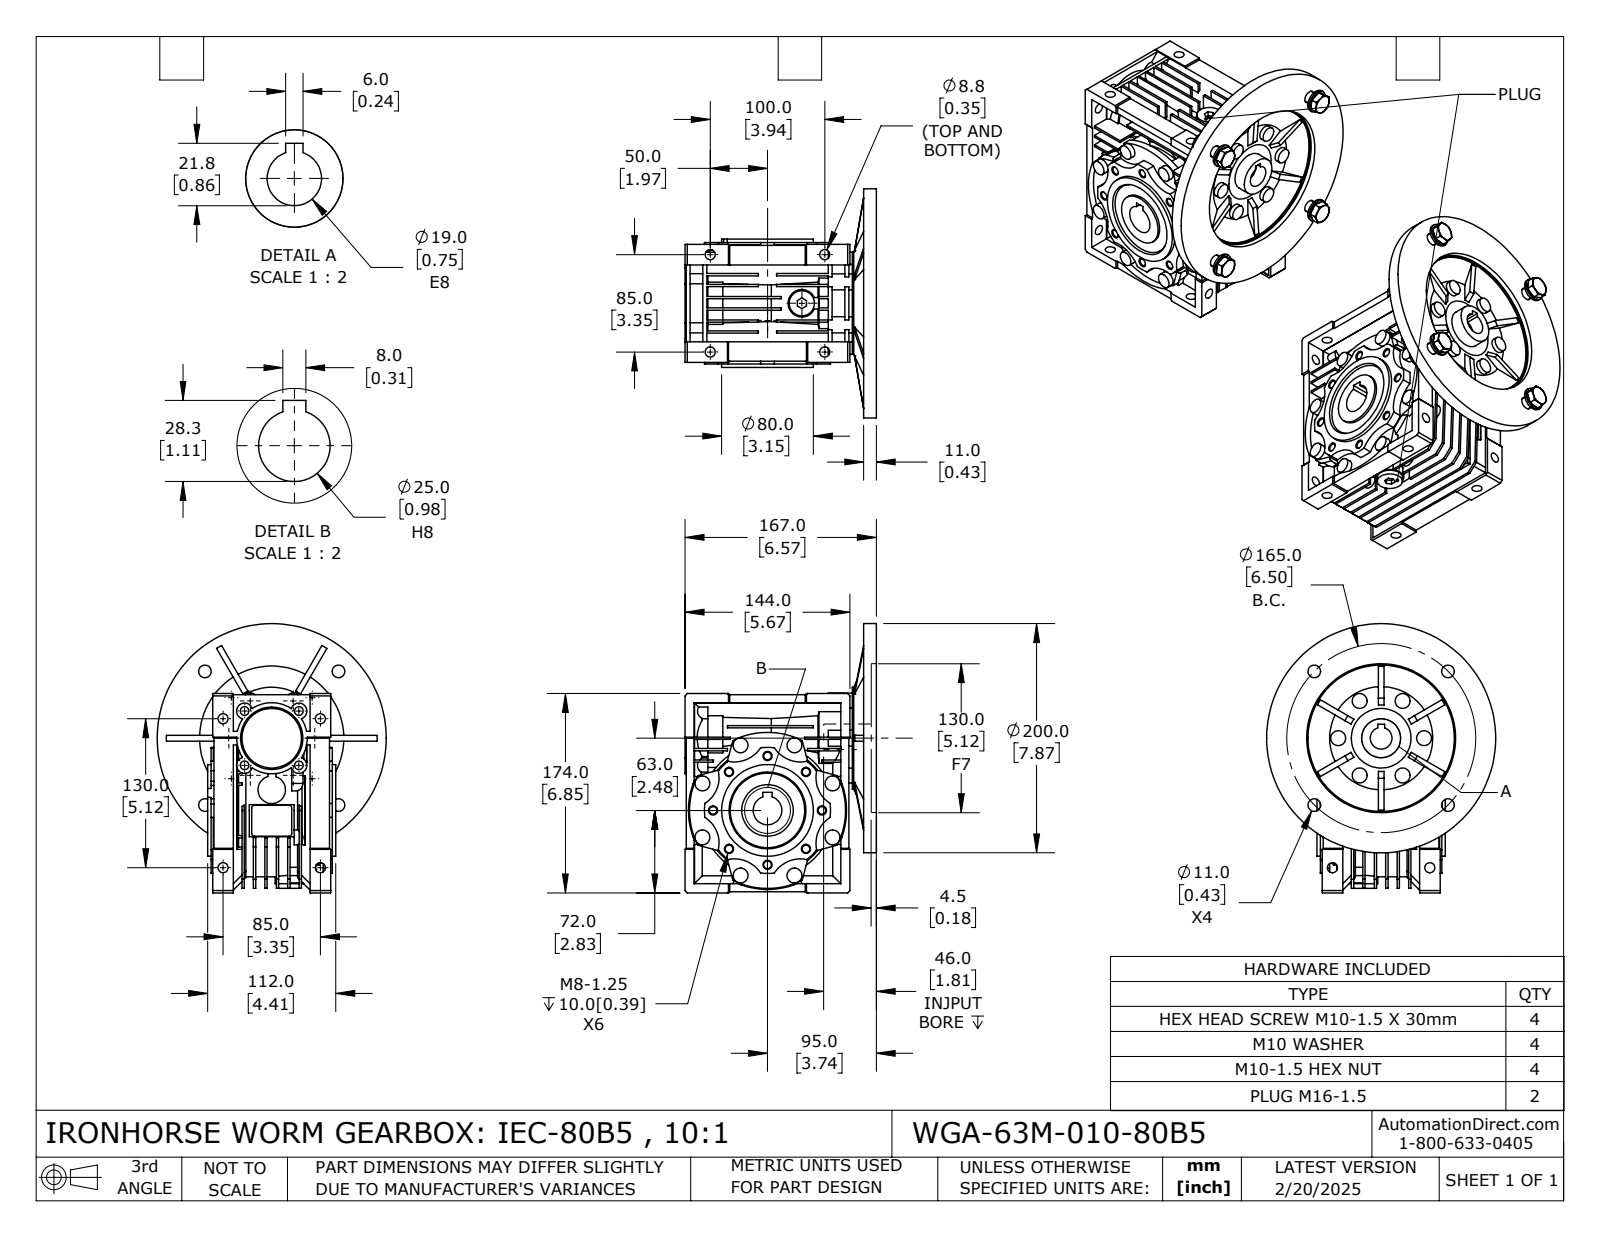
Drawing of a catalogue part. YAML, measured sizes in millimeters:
part_name: "WGA-63M-010-80B5"
step_written_by: "SolidWorks 2024 (CONFIG_CONTROL_DESIGN)"
units: millimeters
bodies: {solids: 20, faces: 1529, planar: 897, cylindrical: 394, other: 238}
overall_size: [235, 200, 183.43]
volume: 2032000
surface_area: 401437
round_holes:
  - {diameter: 6.65, count: 8}
  - {diameter: 8.78, count: 8}
  - {diameter: 7.56, count: 4}
  - {diameter: 8.5, count: 4}
  - {diameter: 10, count: 4}
  - {diameter: 10.5, count: 4}
  - {diameter: 11, count: 4}
  - {diameter: 14.5, count: 2}
  - {diameter: 19, count: 1}
  - {diameter: 20, count: 1}
  - {diameter: 25, count: 1}
  - {diameter: 34, count: 1}
round_bosses_or_shafts:
  - {diameter: 13, count: 14}
  - {diameter: 20, count: 4}
  - {diameter: 16, count: 4}
  - {diameter: 24, count: 3}
  - {diameter: 22, count: 2}
  - {diameter: 15.8, count: 2}
  - {diameter: 13.7, count: 2}
  - {diameter: 200, count: 1}
partial_cylinders:
  - {radius: 7, count: 10}
  - {radius: 27, count: 8}
  - {radius: 2.5, count: 4}
  - {radius: 8.35, count: 1}
  - {radius: 29.5, count: 1}
  - {radius: 30.5, count: 1}
  - {radius: 42, count: 1}
  - {radius: 46, count: 1}
face_to_face_distances: [10, 8, 20, 2, 11, 30, 12, 7, 40, 18]
hole_center_spacings: [36.36, 47.5, 67.18, 87.77, 89.05, 33.5, 47.38, 49]
